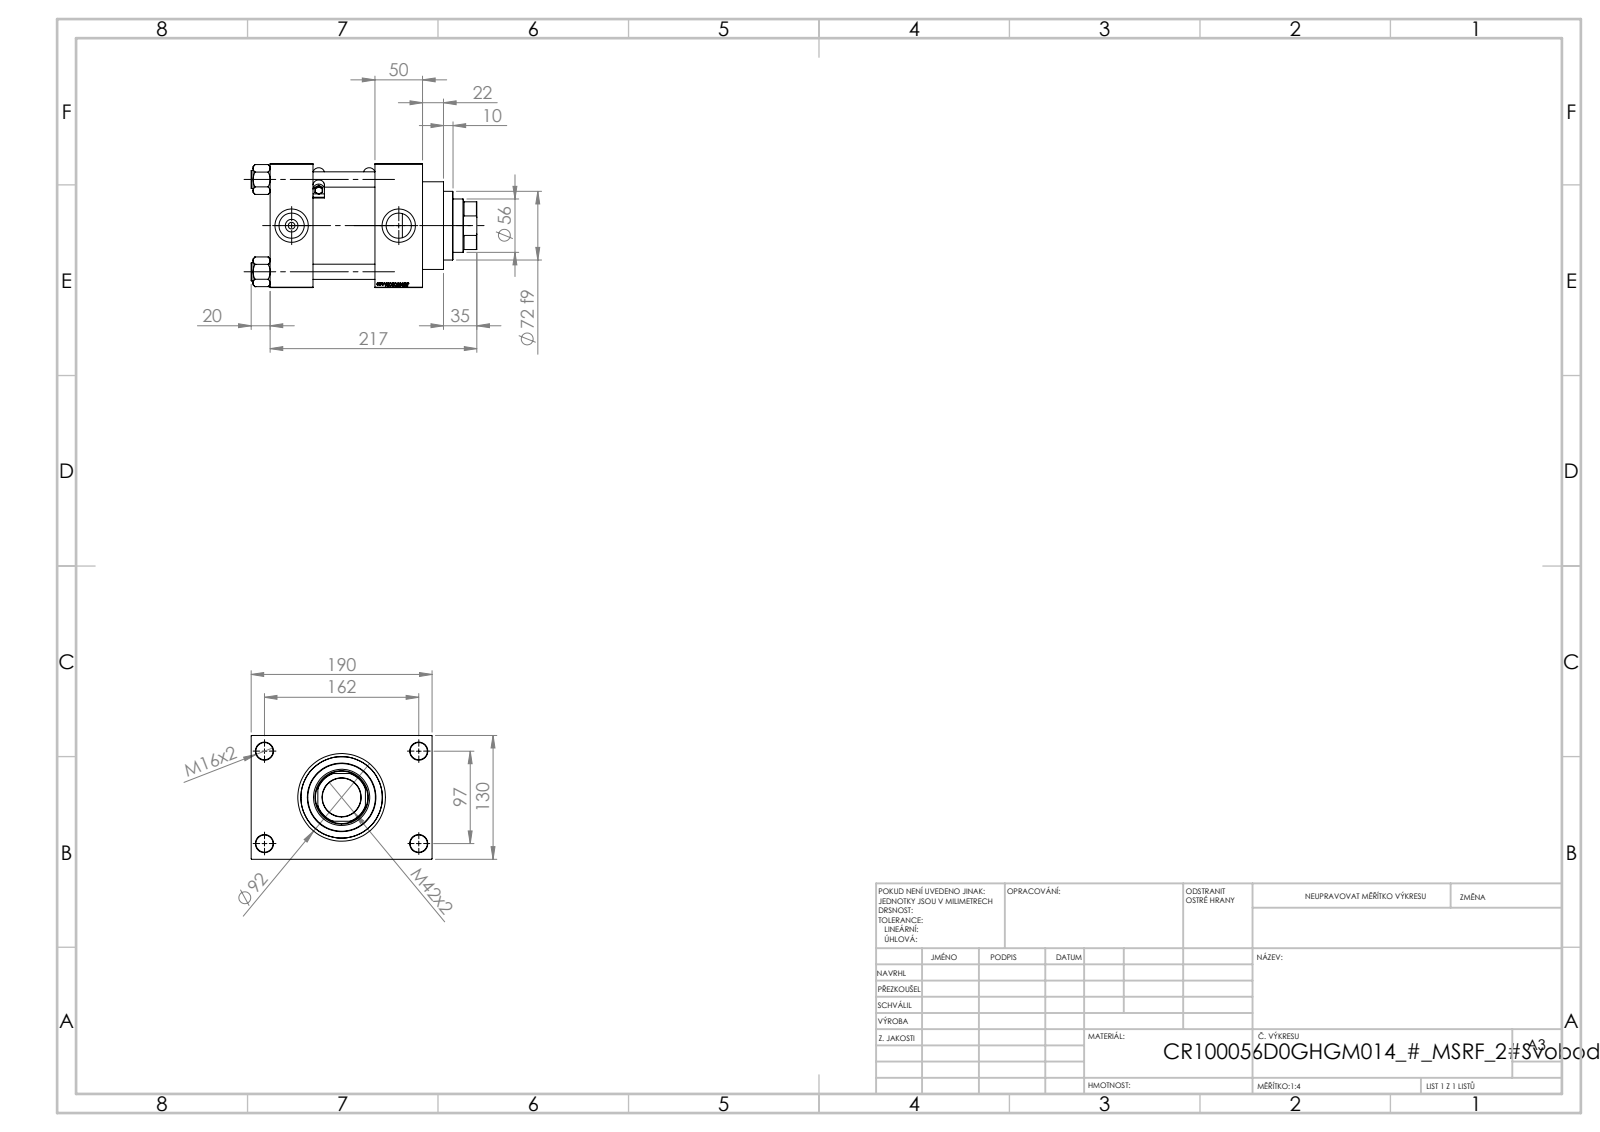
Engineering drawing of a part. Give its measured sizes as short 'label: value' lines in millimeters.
name: V215CR_D_TYCINKA; V215CR_VCP_D; V215_VC_A; MSRF_MSRG1 (+2 more)
written by: SolidWorks 2019 (CONFIG_CONTROL_DESIGN)
unit: mm
bodies: 13 solids, 1215 faces (581 planar, 116 cylindrical, 518 other)
size: 237 × 190 × 130
volume: 2 610 000 mm³; area: 360 927 mm²
holes: 4× ⌀16, 4× ⌀18, 2× ⌀7, 2× ⌀26.44, 2× ⌀35, 1× ⌀40.5, 1× ⌀56, 1× ⌀59, 1× ⌀76, 1× ⌀85.5, 1× ⌀100
bosses: 4× ⌀19, 2× ⌀5, 2× ⌀2.5, 1× ⌀106, 1× ⌀92, 1× ⌀72
rounds: 12× R0.5, 4× R6, 1× R27
face distances: 160, 130, 65, 50, 45, 110, 115, 30, 96, 14
hole spacings: 32.55, 68.52, 94.41, 96.9, 102.27, 129.45, 161.73, 97
